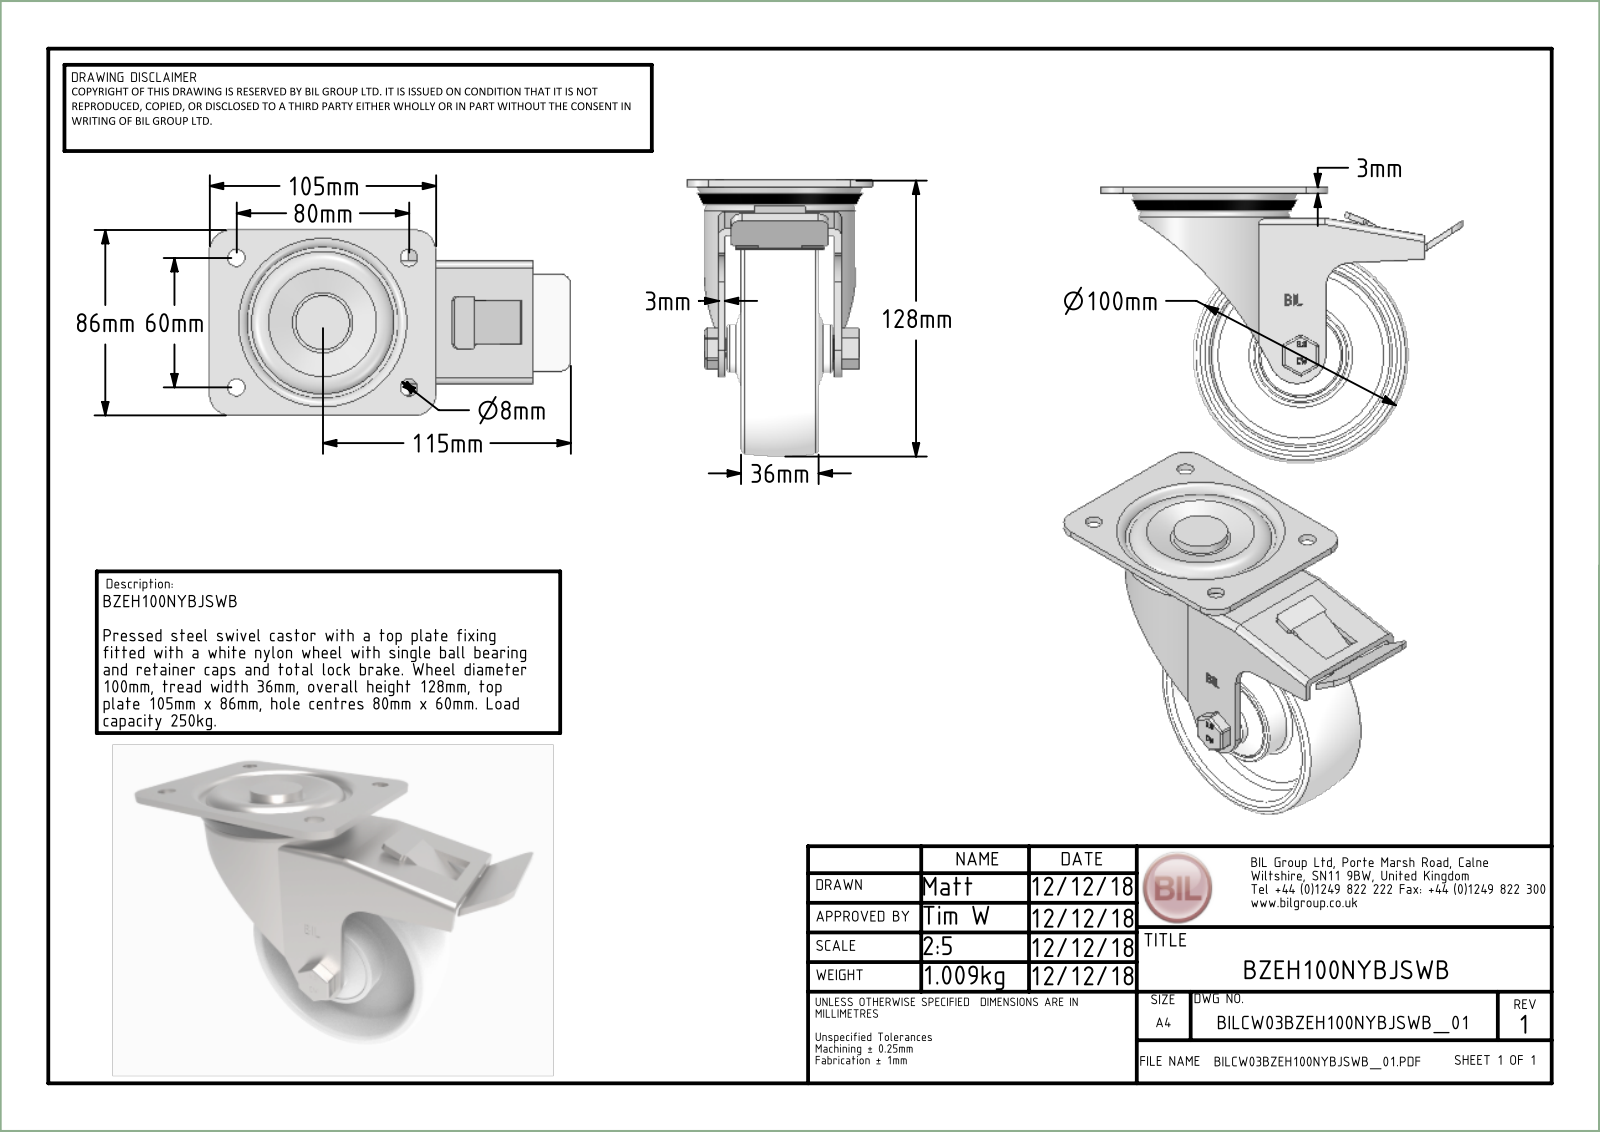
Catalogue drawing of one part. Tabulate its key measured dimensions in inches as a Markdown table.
| quantity | value |
| --- | --- |
| part name | BZEH100NYBJSWB v3; BZEH100ASSWB - 49 v1; ZINC PLATED, PRESSED STEEL TOP PLATE; ZINC PLATED, PRESSED STEEL TOP PLATE Geometry (+7 more) |
| STEP written by | Autodesk Translation Framework v14.4.0.0 (AUTOMOTIVE_DESIGN) |
| units | inches |
| bodies | 45 solids, 978 faces (456 planar, 204 cylindrical, 318 other) |
| overall size | 6.594 × 5.039 × 3.386 |
| volume | 16.36 in³ |
| surface area | 220.3 in² |
| round holes (diameter × count) | 1.181 × 2, 0.315 × 1, 0.394 × 1, 0.402 × 1, 0.472 × 1, 0.591 × 1, 0.787 × 1, 0.886 × 1, 0.984 × 1, 1.22 × 1, 1.26 × 1, 1.28 × 1 |
| round bosses / shafts (diameter × count) | 2.756 × 1, 2.126 × 1, 1.752 × 1, 1.496 × 1, 1.201 × 1, 1.102 × 1, 0.984 × 1, 0.906 × 1 |
| partial cylindrical surfaces (radius × count) | 0.02 × 20, 0.177 × 9, 0.039 × 8, 0.03 × 6, 0.059 × 6, 0.118 × 4, 0.394 × 4, 0.079 × 3 |
| main face-to-face distances | 0.118, 0.197, 0.394, 0.079, 0.039, 0.817, 1.112, 2.047, 0.935, 1.23 |
